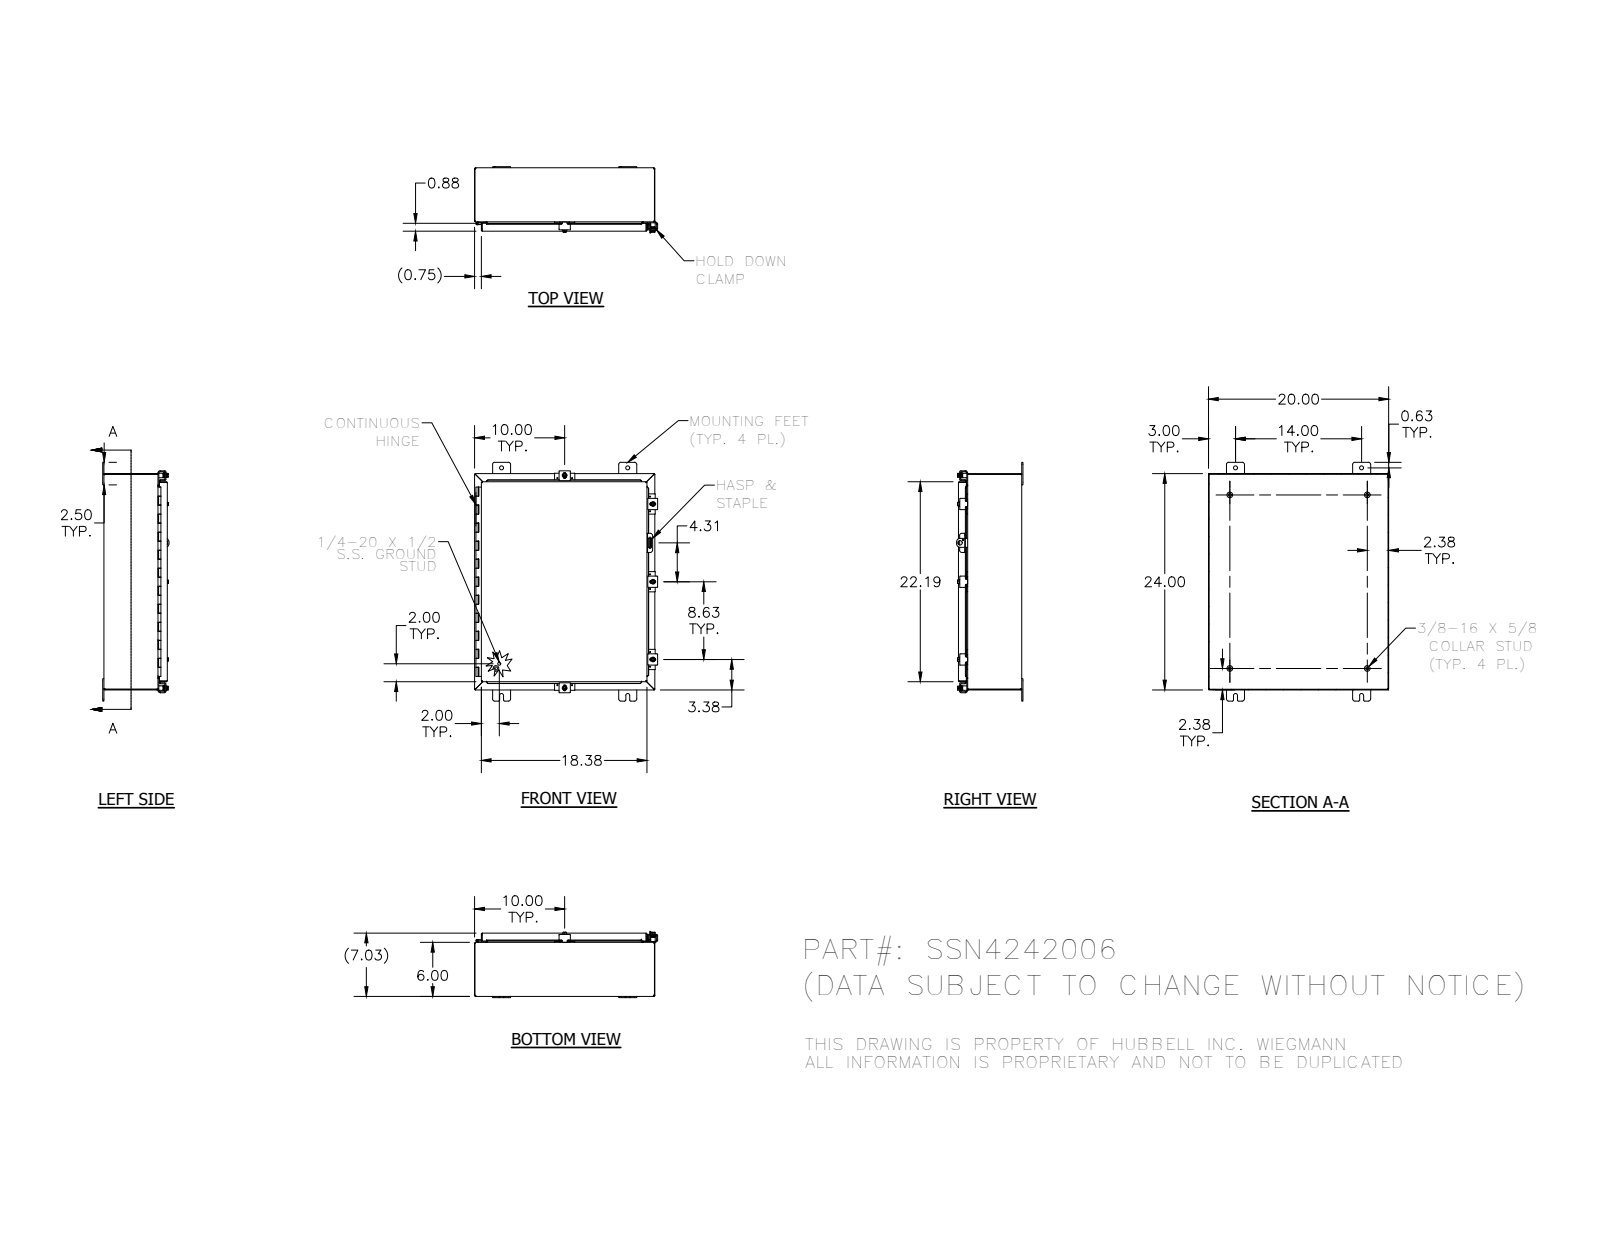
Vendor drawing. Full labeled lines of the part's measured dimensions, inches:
Part name (STEP PRODUCT): HFW30825-3_1; 38859_1; HFW30825-4_1; 328138_1 (+8 more)
STEP written by: SolidWorks 2014 (AUTOMOTIVE_DESIGN)
Units: inches
Bodies: 42 solids, 1674 faces (650 planar, 737 cylindrical, 287 other)
Overall size (bounding box): 26.5 × 20.311 × 7.355
Volume: 140.3 in³ · Surface area: 3 664 in²
Round holes (diameter × count): ⌀0.11 ×10, ⌀0.211 ×5, ⌀0.281 ×5, ⌀0.3 ×5, ⌀0.438 ×4, ⌀0.125 ×1, ⌀0.156 ×1, ⌀0.5 ×1
Round bosses / shafts (diameter × count): ⌀0.25 ×7, ⌀0.52 ×5, ⌀0.5 ×5, ⌀0.35 ×5, ⌀0.625 ×4, ⌀0.33 ×4, ⌀0.115 ×2, ⌀0.337 ×1
Partial cylindrical surfaces — rounded edges, fillets, slot ends (radius × count): R0.03 ×61, R0.125 ×35, R0.25 ×31, R0.031 ×23, R0.105 ×23, R0.062 ×13, R0.141 ×10, R0.07 ×8
Main face-to-face distances: 0.074, 6.959, 6.885, 7.033, 19.926, 23.926, 5.926, 1.033, 19.852, 20
Hole centre spacings: 0.876, 23.303, 1.625, 7.82, 8.625, 8.625, 9.443, 17.25
